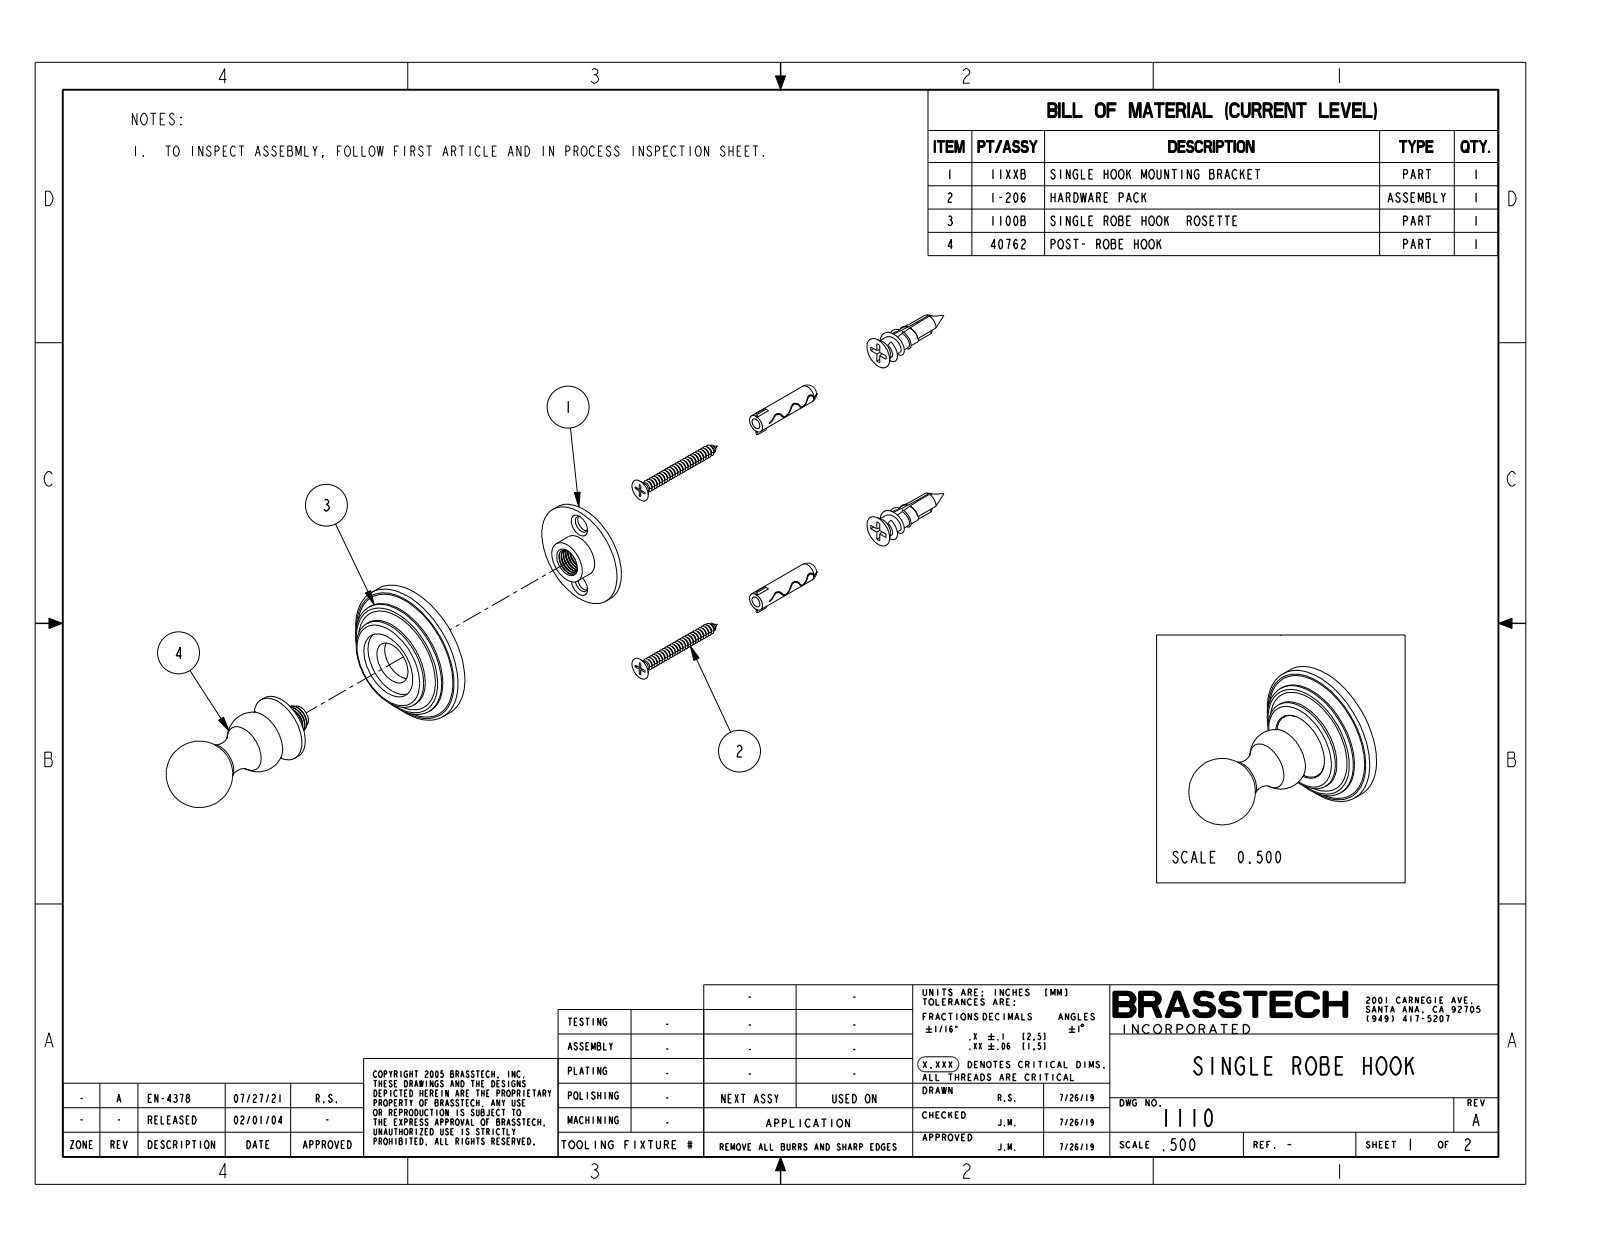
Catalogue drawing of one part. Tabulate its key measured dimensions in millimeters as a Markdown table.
| quantity | value |
| --- | --- |
| part name | 1110 |
| STEP written by | CREO PARAMETRIC BY PTC INC, 2018400 (AUTOMOTIVE_DESIGN) |
| units | millimeters |
| bodies | 1 solid, 35 faces (5 planar, 12 cylindrical, 18 other) |
| overall size | 62.7 × 50 × 50 |
| volume | 31 040 mm³ |
| surface area | 8 239 mm² |
| round holes (diameter × count) | 24.1 × 1 |
| round bosses / shafts (diameter × count) | 50 × 1, 42 × 1, 32.8 × 1, 23.6 × 1, 13.6 × 1 |
| main face-to-face distances | 12.7, 8.4, 4.3, 4.4, 4.1, 8.3, 10.7, 6.3, 2.3, 2 |
